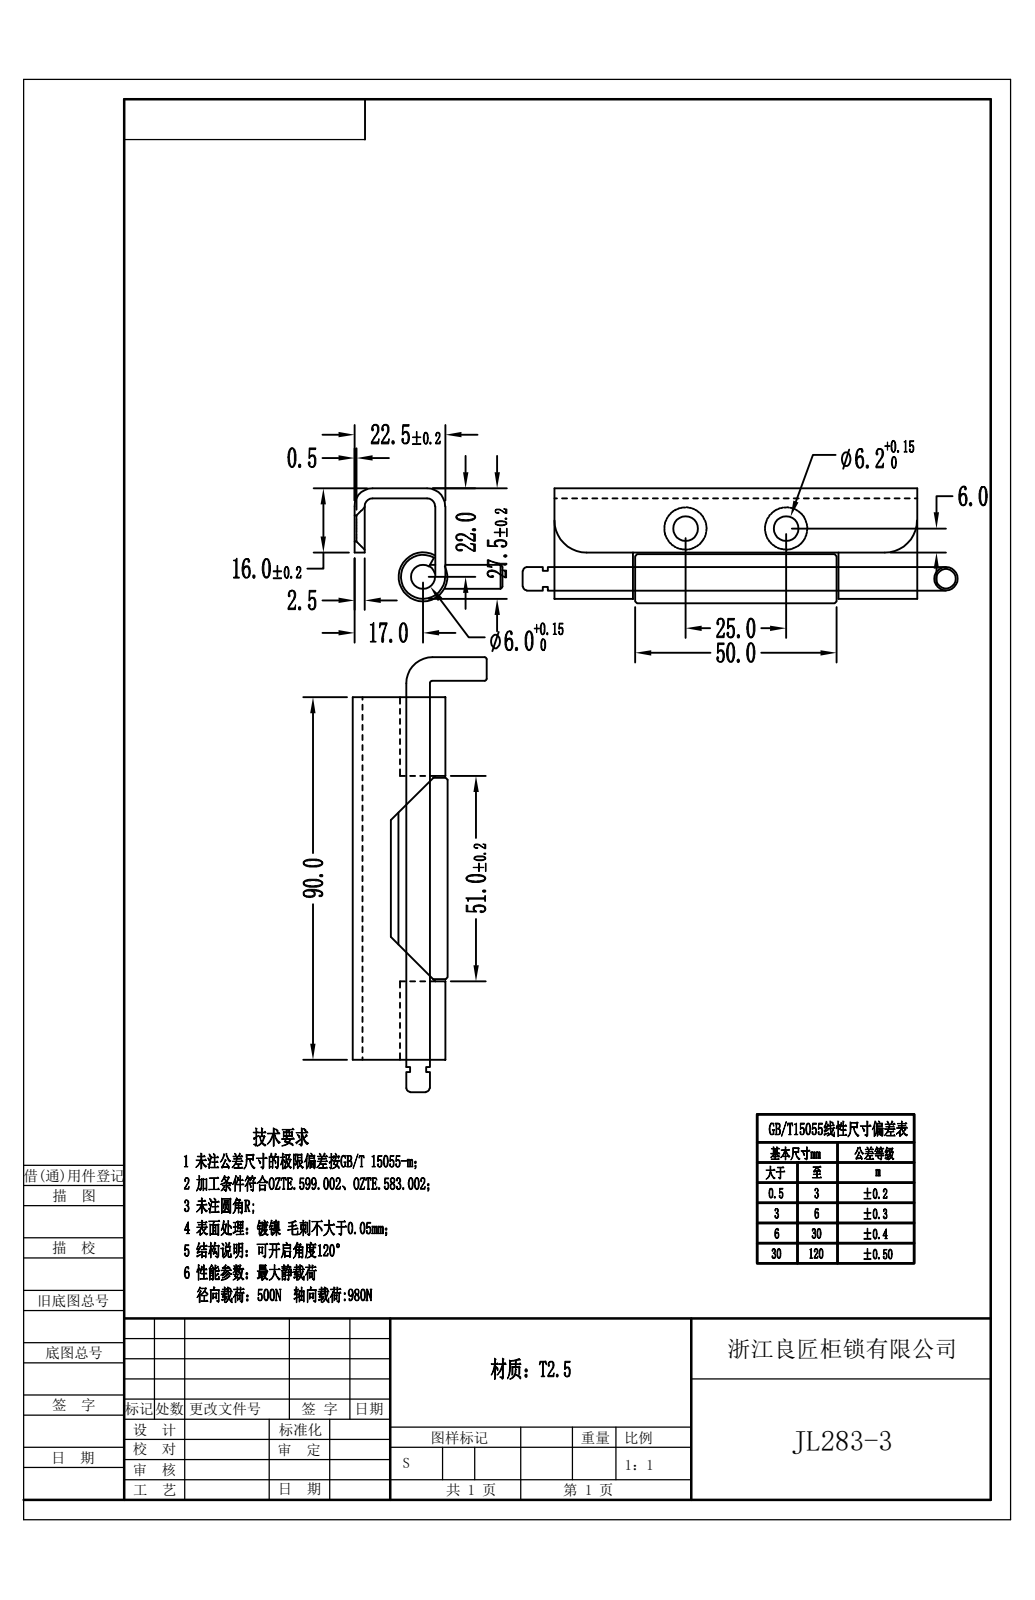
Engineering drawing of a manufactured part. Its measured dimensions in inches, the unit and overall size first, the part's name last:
Units: inches
Overall size (bounding box): 4.252 × 1.537 × 0.909
Round holes (diameter × count): ⌀0.244 ×2, ⌀0.236 ×1
Round bosses / shafts (diameter × count): ⌀0.232 ×2, ⌀0.48 ×1, ⌀0.433 ×1, ⌀0.157 ×1
Partial cylindrical surfaces — rounded edges, fillets, slot ends (radius × count): R0.079 ×2, R0.177 ×2
Main face-to-face distances: 0.098, 0.787, 0.886, 0.689, 0.909, 0.811, 0.122, 0.024, 0.531, 0.63
Hole centre spacings: 0.984
Volume: 0.446 in³ · Surface area: 26.21 in²
Bodies: 2 solids, 53 faces (23 planar, 22 cylindrical, 8 other)
STEP written by: Rhino 8.5 (CONFIG_CONTROL_DESIGN)
